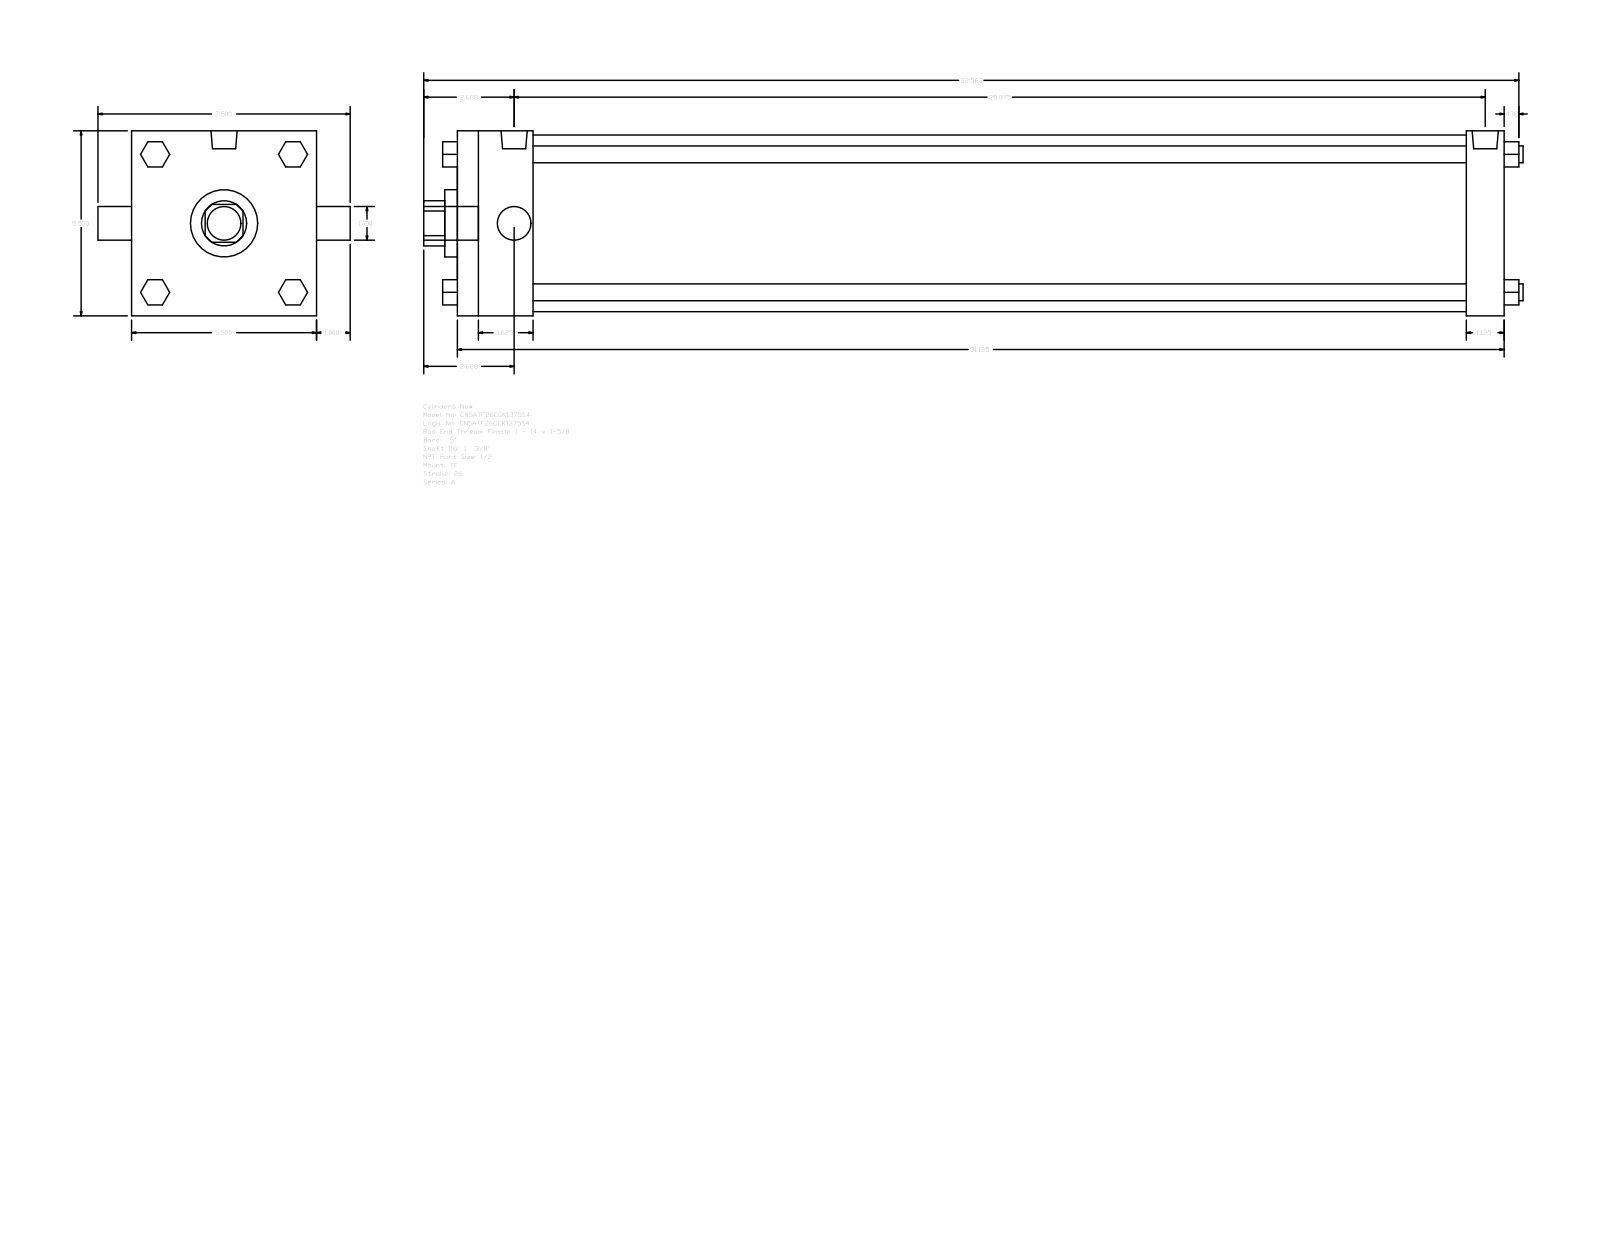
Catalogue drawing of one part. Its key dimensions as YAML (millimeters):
part_name: "A_TF__0500_1.375"
step_written_by: "GSSL Pune (CONFIG_CONTROL_DESIGN)"
units: millimeters
bodies: {solids: 0, faces: 120, planar: 92, cylindrical: 28, other: 0}
overall_size: [830.26, 190.5, 139.7]
round_holes:
  - {diameter: 25.4, count: 1}
  - {diameter: 34.92, count: 1}
  - {diameter: 50.8, count: 1}
  - {diameter: 133.35, count: 1}
round_bosses_or_shafts:
  - {diameter: 12.7, count: 4}
  - {diameter: 8.73, count: 3}
  - {diameter: 19.77, count: 2}
  - {diameter: 25.4, count: 1}
partial_cylinders:
  - {radius: 17.06, count: 1}
face_to_face_distances: [139.7, 790.58, 28.58, 762, 57.15, 704.85, 733.43, 19.05, 52.07, 90.18]
